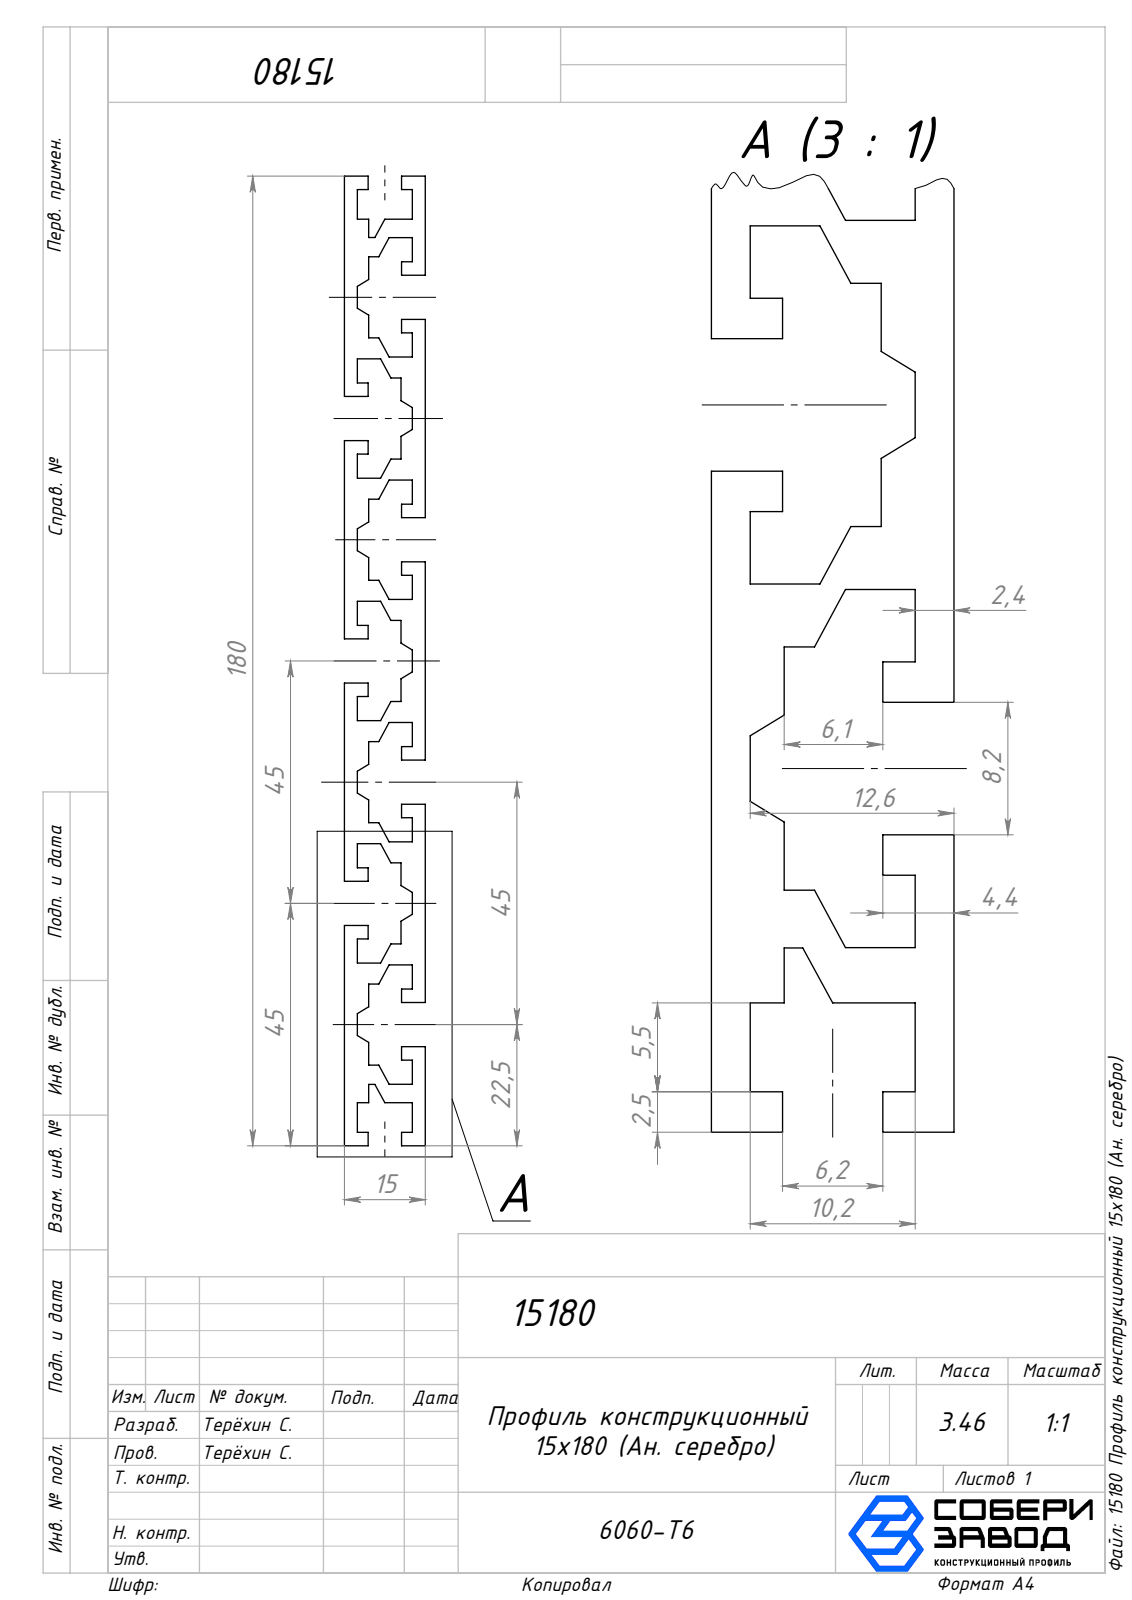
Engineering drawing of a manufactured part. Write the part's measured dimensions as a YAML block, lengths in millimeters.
part_name: "15180X Профиль конструкционный 15х180 (Без покрытия)"
step_written_by: "SolidWorks 2025 (AUTOMOTIVE_DESIGN)"
units: millimeters
bodies: {solids: 1, faces: 170, planar: 170, cylindrical: 0, other: 0}
overall_size: [1000, 180, 15]
volume: 1281000
surface_area: 846319
face_to_face_distances: [15, 2.4, 12.6, 8.2, 4.5, 10.5, 2.1, 8.1, 10.2, 22.5]
